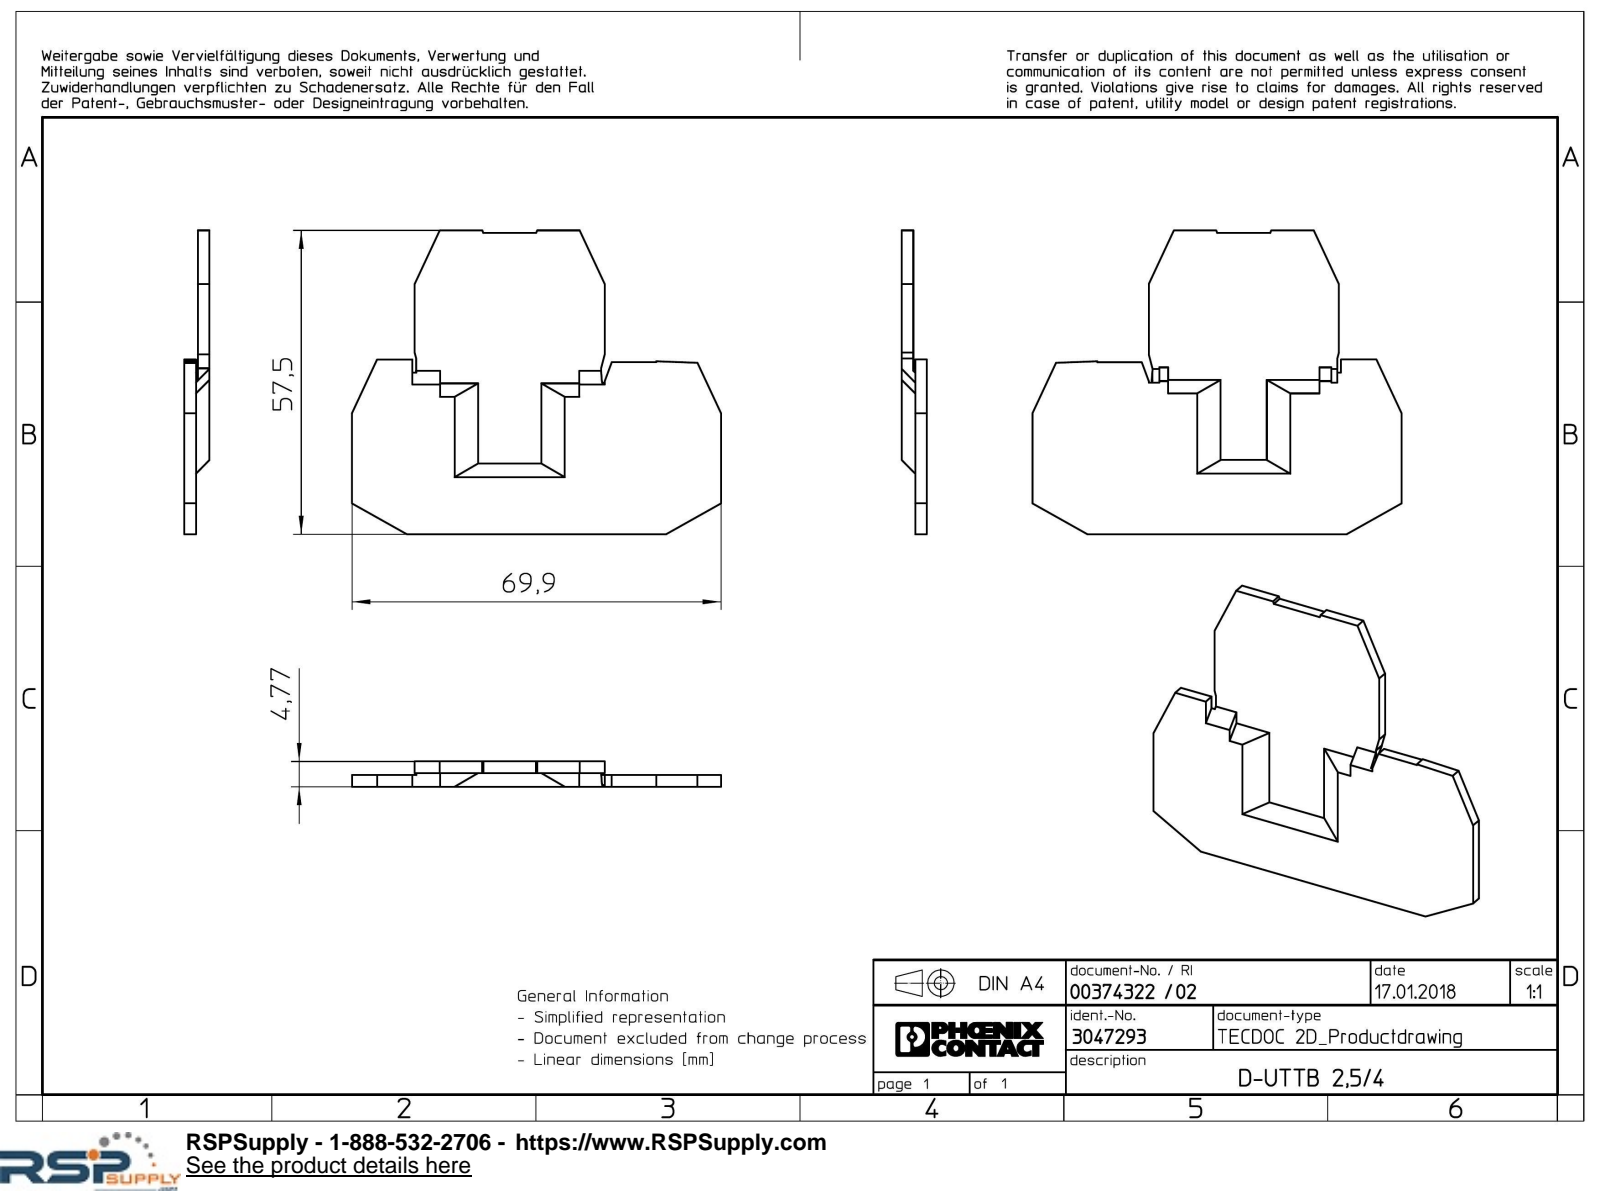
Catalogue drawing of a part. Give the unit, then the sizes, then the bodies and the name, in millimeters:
Units: millimetres
Overall size (bounding box): 69.9 × 57.5 × 4.78
Main face-to-face distances: 2.2, 2.57, 0.37, 4.77, 1.1, 10.73, 9.63, 12.4, 1.67, 69.9
Volume: 6 457 mm³ · Surface area: 6 709 mm²
Bodies: 1 solid, 56 faces (56 planar, 0 cylindrical, 0 other)
Part name (STEP PRODUCT): D_UTTB_2.5_4-select
STEP written by: Creo Elements/Direct Modeling 20.1A 29-Sep-2018 (C) Parametric Technology GmbH (AUTOMOTIVE_DESIGN)
